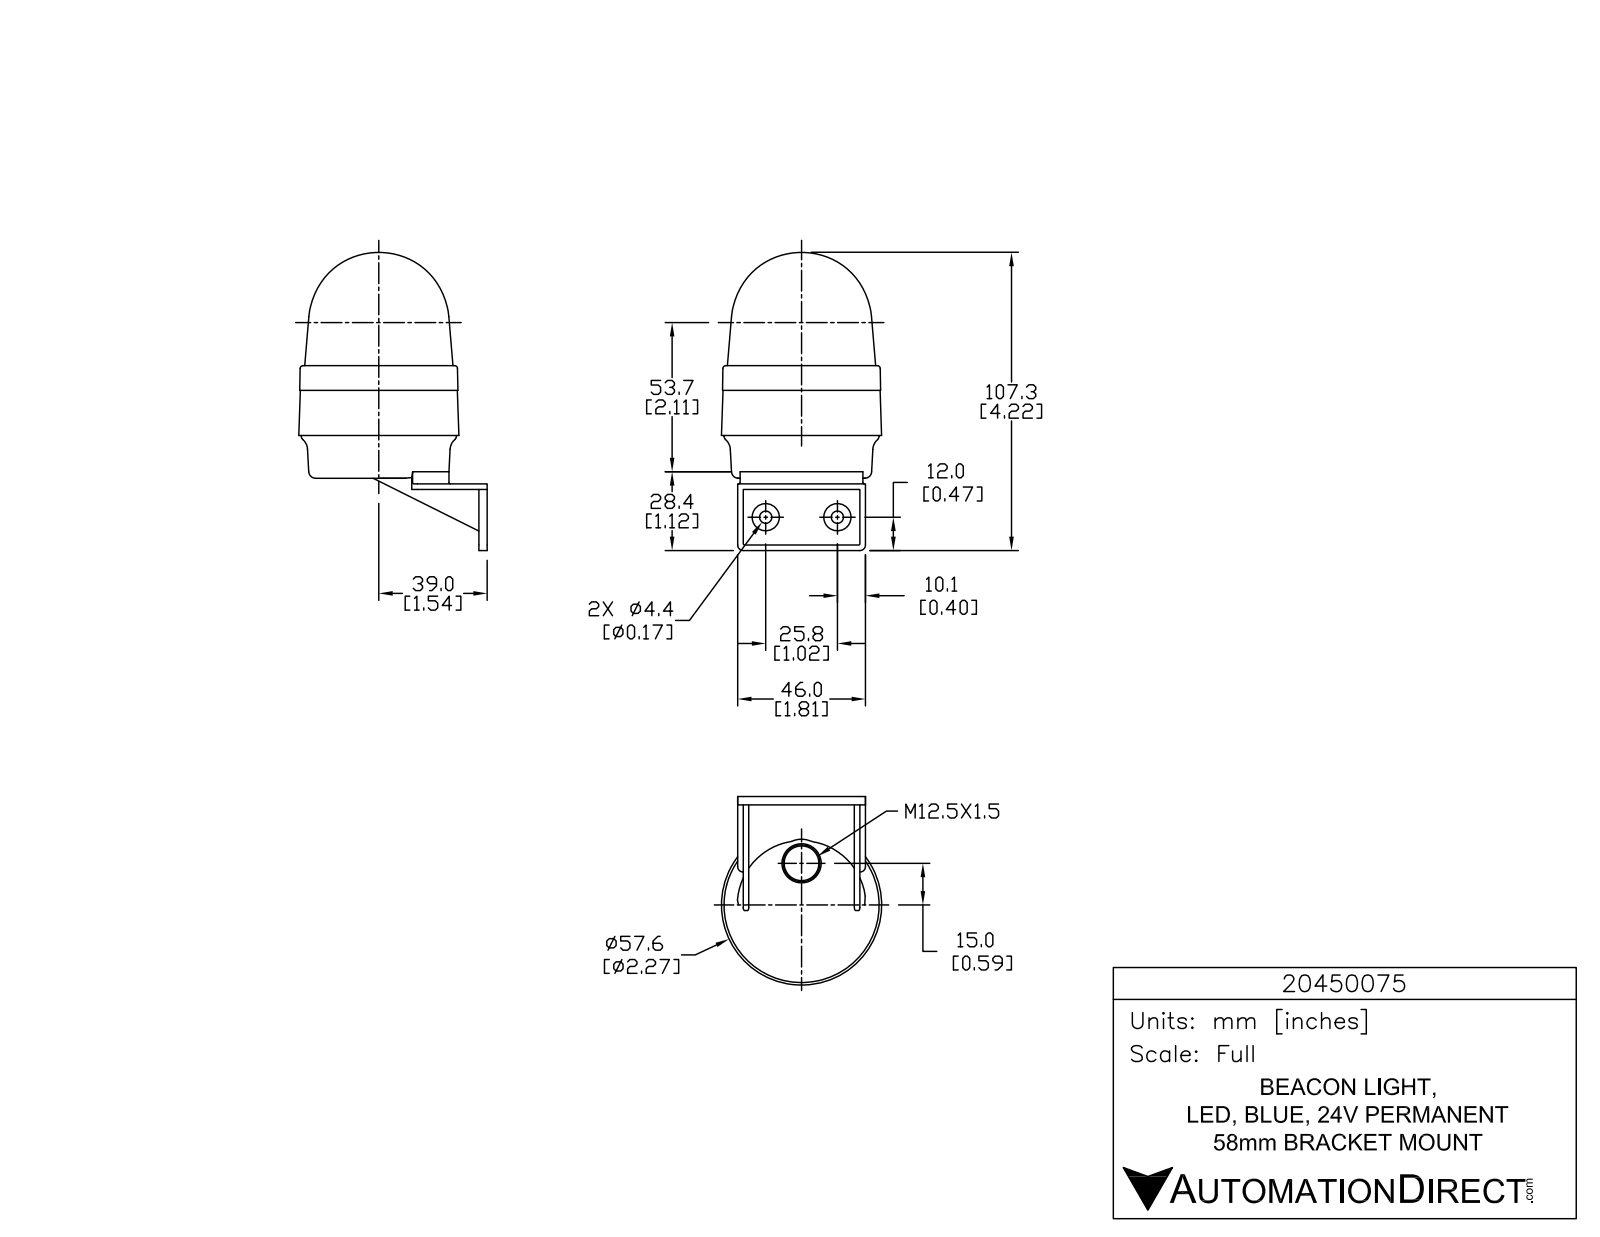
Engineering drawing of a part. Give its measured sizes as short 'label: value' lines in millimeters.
name: 20450075
written by: SolidWorks 2015 (AUTOMOTIVE_DESIGN)
unit: mm
bodies: 1 solid, 828 faces (551 planar, 179 cylindrical, 98 other)
size: 107.3 × 72.4 × 61.1
volume: 168 300 mm³; area: 21 540 mm²
holes: 3× ⌀1, 2× ⌀4.4
bosses: 3× ⌀5.7, 3× ⌀1.4, 2× ⌀9.8, 1× ⌀55.8
rounds: 6× R0.2, 6× R0.2, 6× R0.2, 6× R0.5, 6× R3.3, 4× R2, 3× R0.1, 3× R0.1
face distances: 2, 4, 40, 42, 1, 3, 38, 22, 24, 19.4
hole spacings: 25.8
